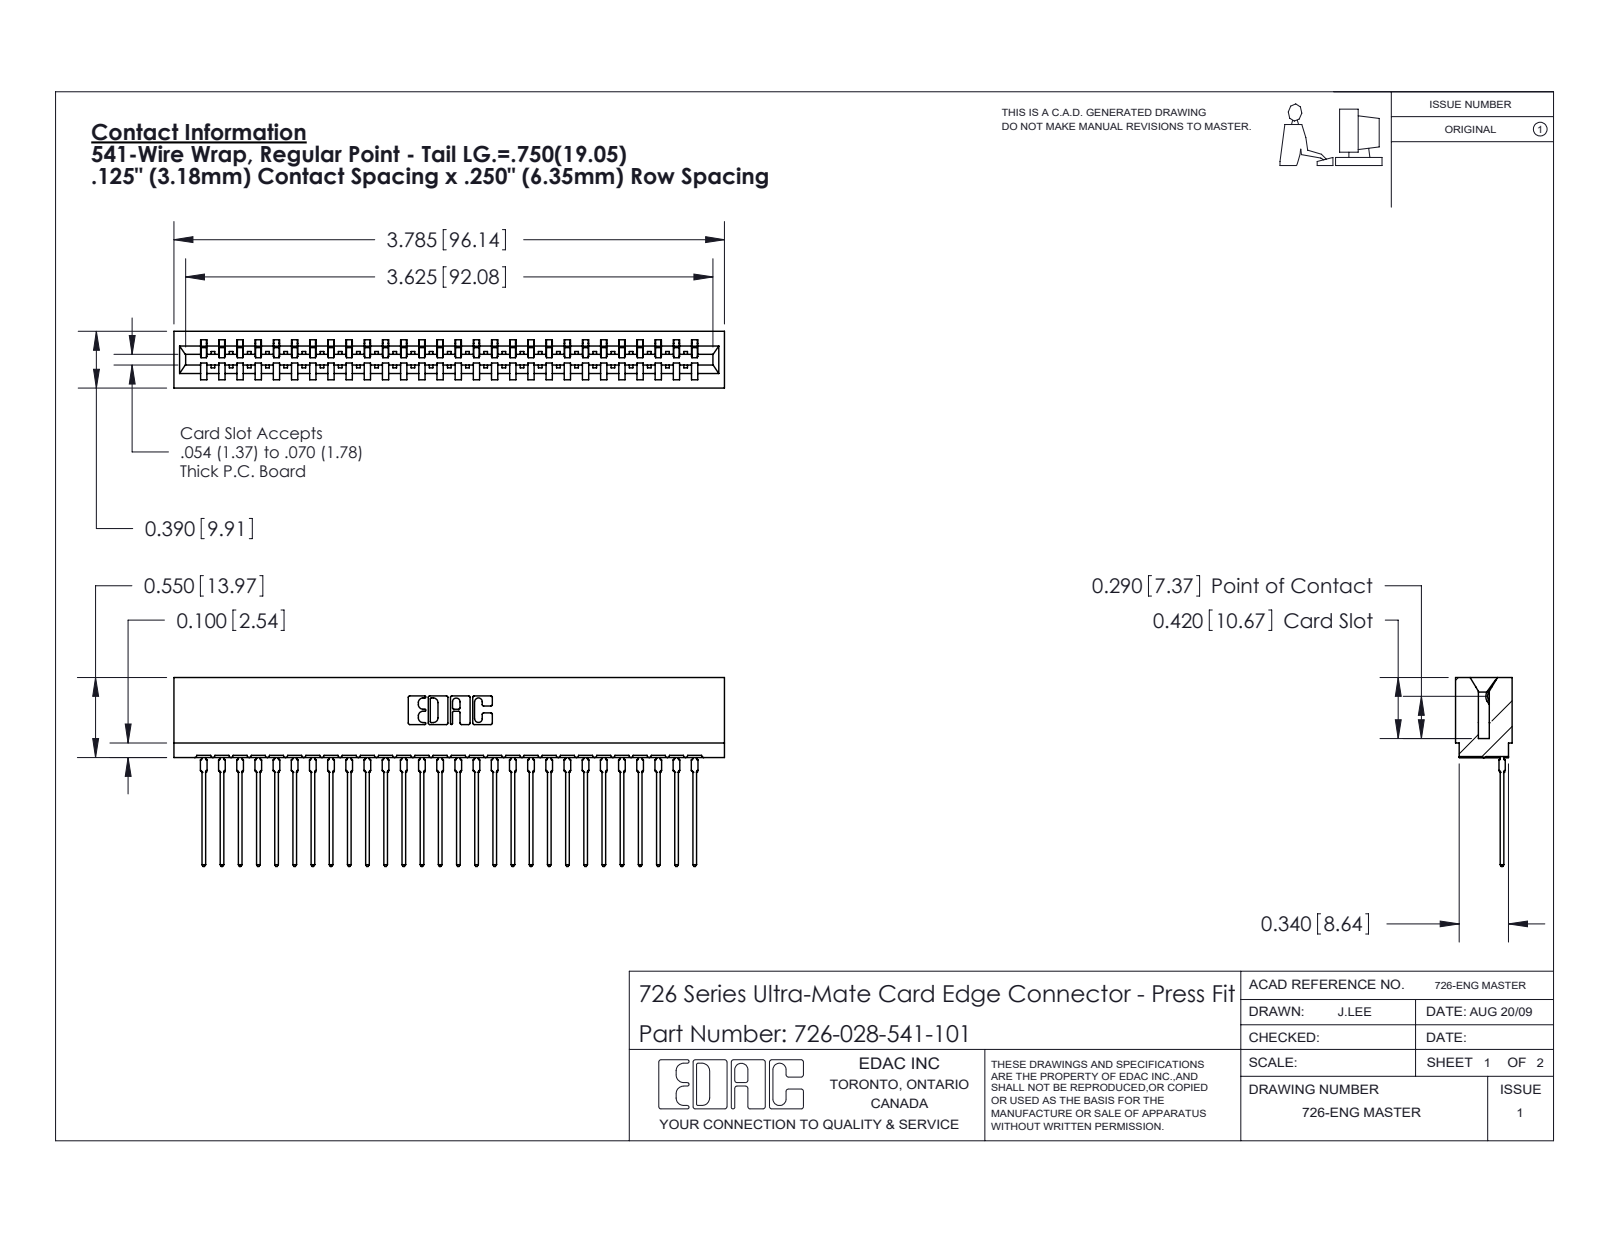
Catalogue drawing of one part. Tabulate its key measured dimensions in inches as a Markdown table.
| quantity | value |
| --- | --- |
| part name | 726 Part_.515 Slot Depth - 01; 746-292-001_541; 726-028-541-101 |
| STEP written by | SolidWorks 2020 (CONFIG_CONTROL_DESIGN) |
| units | inches |
| bodies | 29 solids, 3121 faces (1819 planar, 574 cylindrical, 728 other) |
| overall size | 3.785 × 1.299 × 0.39 |
| volume | 0.537 in³ |
| surface area | 21.53 in² |
| partial cylindrical surfaces (radius × count) | 0.021 × 56, 0.015 × 29, 0.01 × 22, 0.007 × 6, 0.031 × 6, 0.005 × 4, 0.011 × 4, 0.026 × 3 |
| main face-to-face distances | 0.057, 0.333, 0.39, 0.25, 0.025, 0.307, 0.083, 0.275, 0.5, 0.365 |
